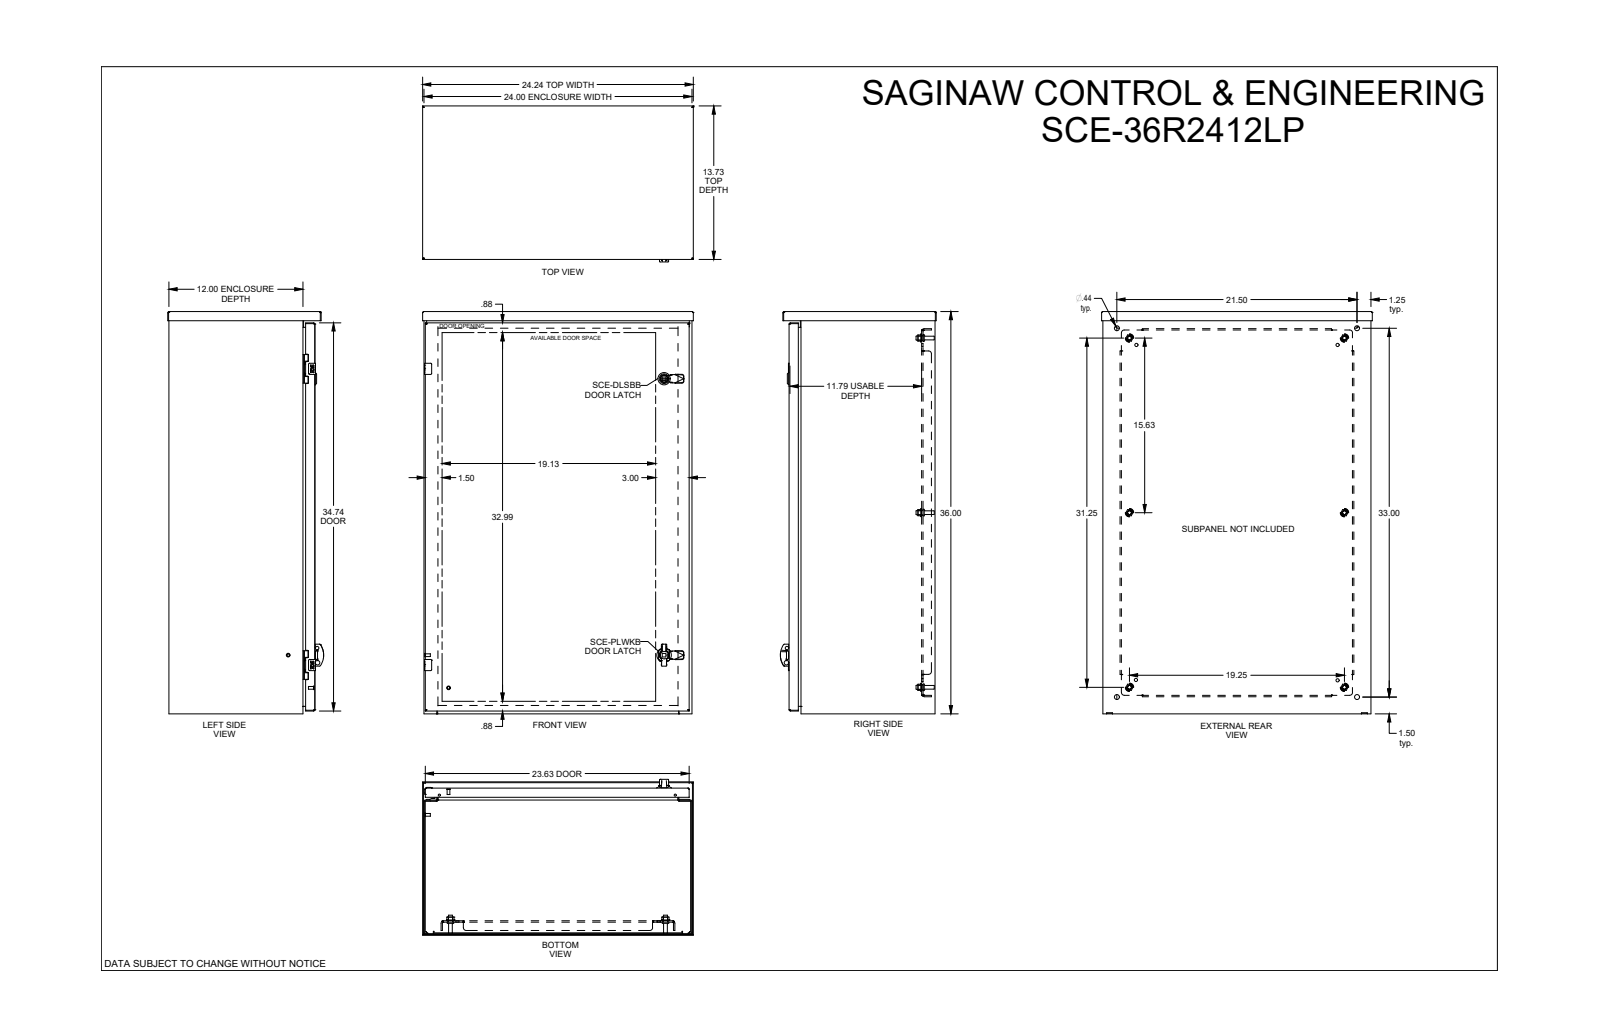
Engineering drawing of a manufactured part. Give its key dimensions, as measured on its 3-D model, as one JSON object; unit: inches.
{"part_name": "SCE-36R2412LP", "step_written_by": "SolidWorks 2019 (CONFIG_CONTROL_DESIGN)", "units": "inches", "bodies": {"solids": 0, "faces": 2607, "planar": 1214, "cylindrical": 875, "other": 518}, "overall_size": [36, 24.236, 13.957], "round_holes": [[0.367, 6], [0.5, 6], [0.172, 4], [0.205, 4], [0.244, 4], [0.266, 4], [0.281, 4], [0.375, 4], [0.438, 4], [0.04, 2], [0.156, 2], [0.188, 2]], "round_bosses_or_shafts": [[0.366, 6], [0.332, 6], [0.17, 6], [0.25, 4], [0.24, 4], [0.196, 3], [0.866, 2], [0.802, 2]], "partial_cylinders_radius": [[0.015, 70], [0.012, 60], [0.06, 46], [0.01, 38], [0.02, 24], [0.117, 19], [0.042, 17], [0.03, 15]], "face_to_face_distances": [0.075, 0.075, 12.918, 12.993, 23.925, 13.068, 12.993, 0.125, 1, 11.918], "hole_center_spacings": [26.5, 0.494, 0.875, 1.426, 15.625, 16.538, 20.394, 24.793]}
